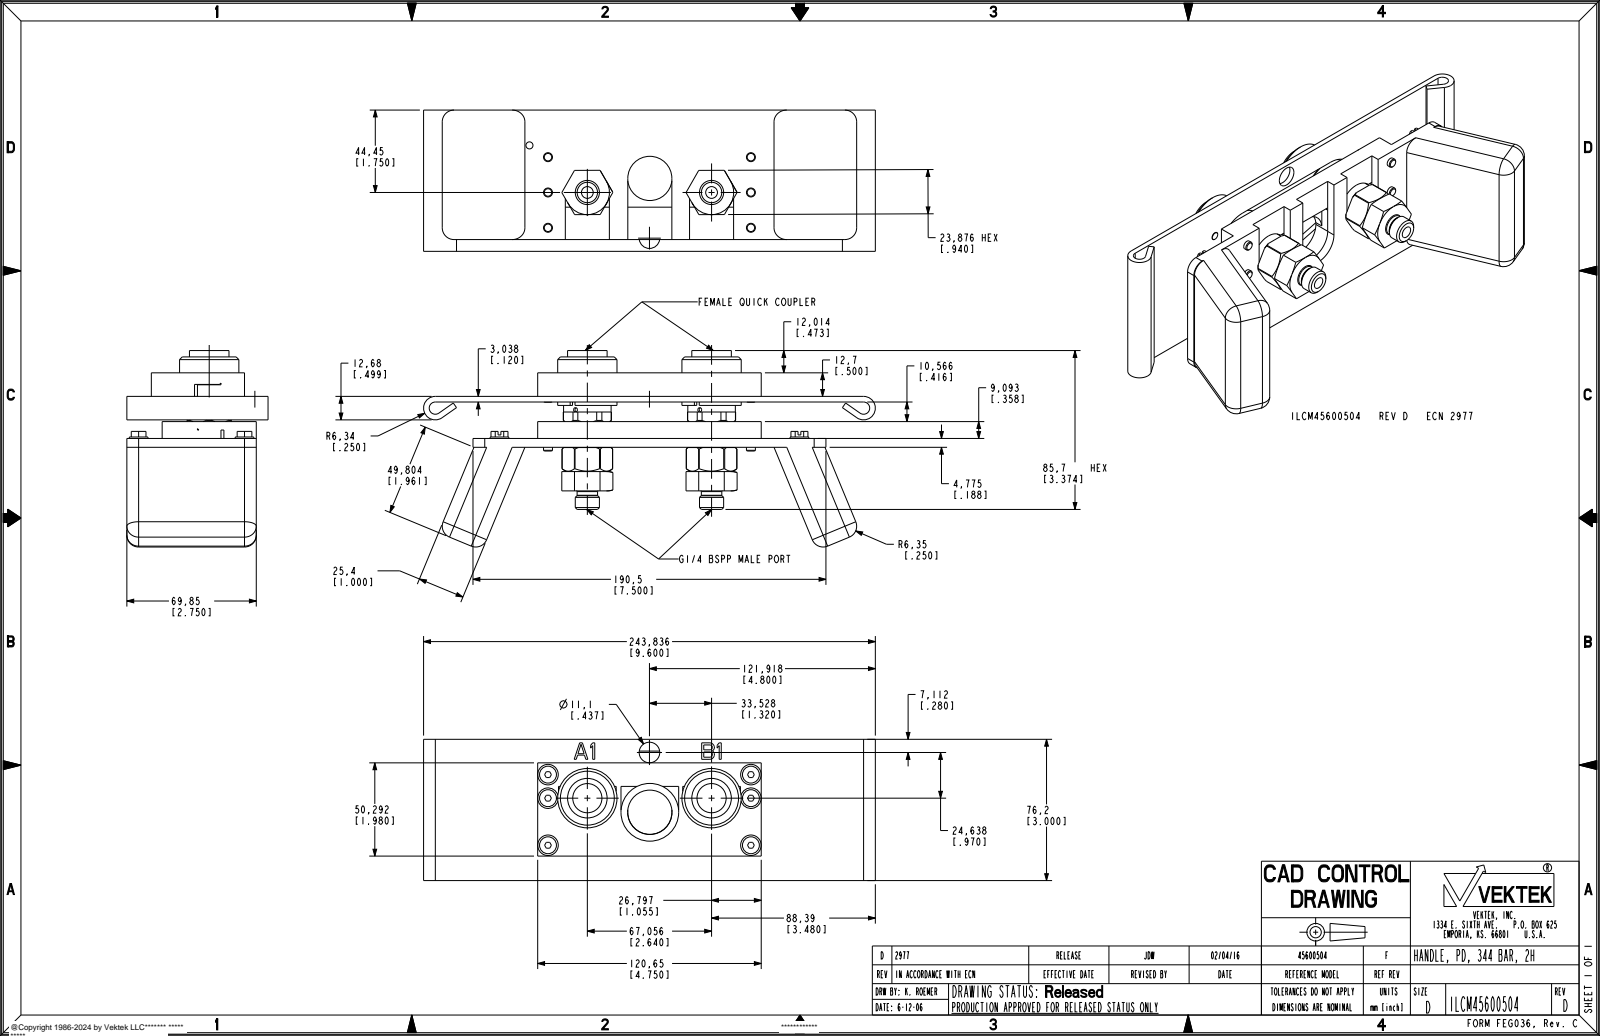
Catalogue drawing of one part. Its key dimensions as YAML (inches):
part_name: "ILCM45600504"
step_written_by: "PRO/ENGINEER BY PARAMETRIC TECHNOLOGY CORPORATION, 2013320 (AUTOMOTIVE_DESIGN)"
units: inches
bodies: {solids: 1, faces: 868, planar: 474, cylindrical: 214, other: 180}
overall_size: [9.6, 4.172, 3]
volume: 27.95
surface_area: 209.7
round_holes:
  - {diameter: 0.219, count: 10}
  - {diameter: 0.264, count: 4}
  - {diameter: 0.942, count: 3}
  - {diameter: 1.226, count: 3}
  - {diameter: 0.094, count: 2}
  - {diameter: 0.173, count: 2}
  - {diameter: 0.22, count: 2}
  - {diameter: 0.25, count: 2}
  - {diameter: 0.509, count: 2}
  - {diameter: 0.62, count: 2}
  - {diameter: 1.06, count: 2}
  - {diameter: 0.15, count: 1}
round_bosses_or_shafts:
  - {diameter: 0.19, count: 12}
  - {diameter: 0.396, count: 4}
  - {diameter: 1.26, count: 2}
  - {diameter: 1.195, count: 2}
  - {diameter: 1.01, count: 2}
  - {diameter: 0.923, count: 2}
  - {diameter: 0.84, count: 2}
  - {diameter: 0.513, count: 2}
partial_cylinders:
  - {radius: 0.25, count: 20}
  - {radius: 0.468, count: 3}
  - {radius: 0.68, count: 3}
  - {radius: 0.059, count: 2}
  - {radius: 0.13, count: 2}
  - {radius: 0.25, count: 2}
  - {radius: 0.511, count: 2}
  - {radius: 0.537, count: 2}
face_to_face_distances: [0.12, 0.894, 0.774, 1.081, 0.962, 0.188, 0.5, 1, 0.535, 0.416]
hole_center_spacings: [4.312, 0.25, 0.75, 1.123, 1.275, 1.5, 1.82, 2.25]
